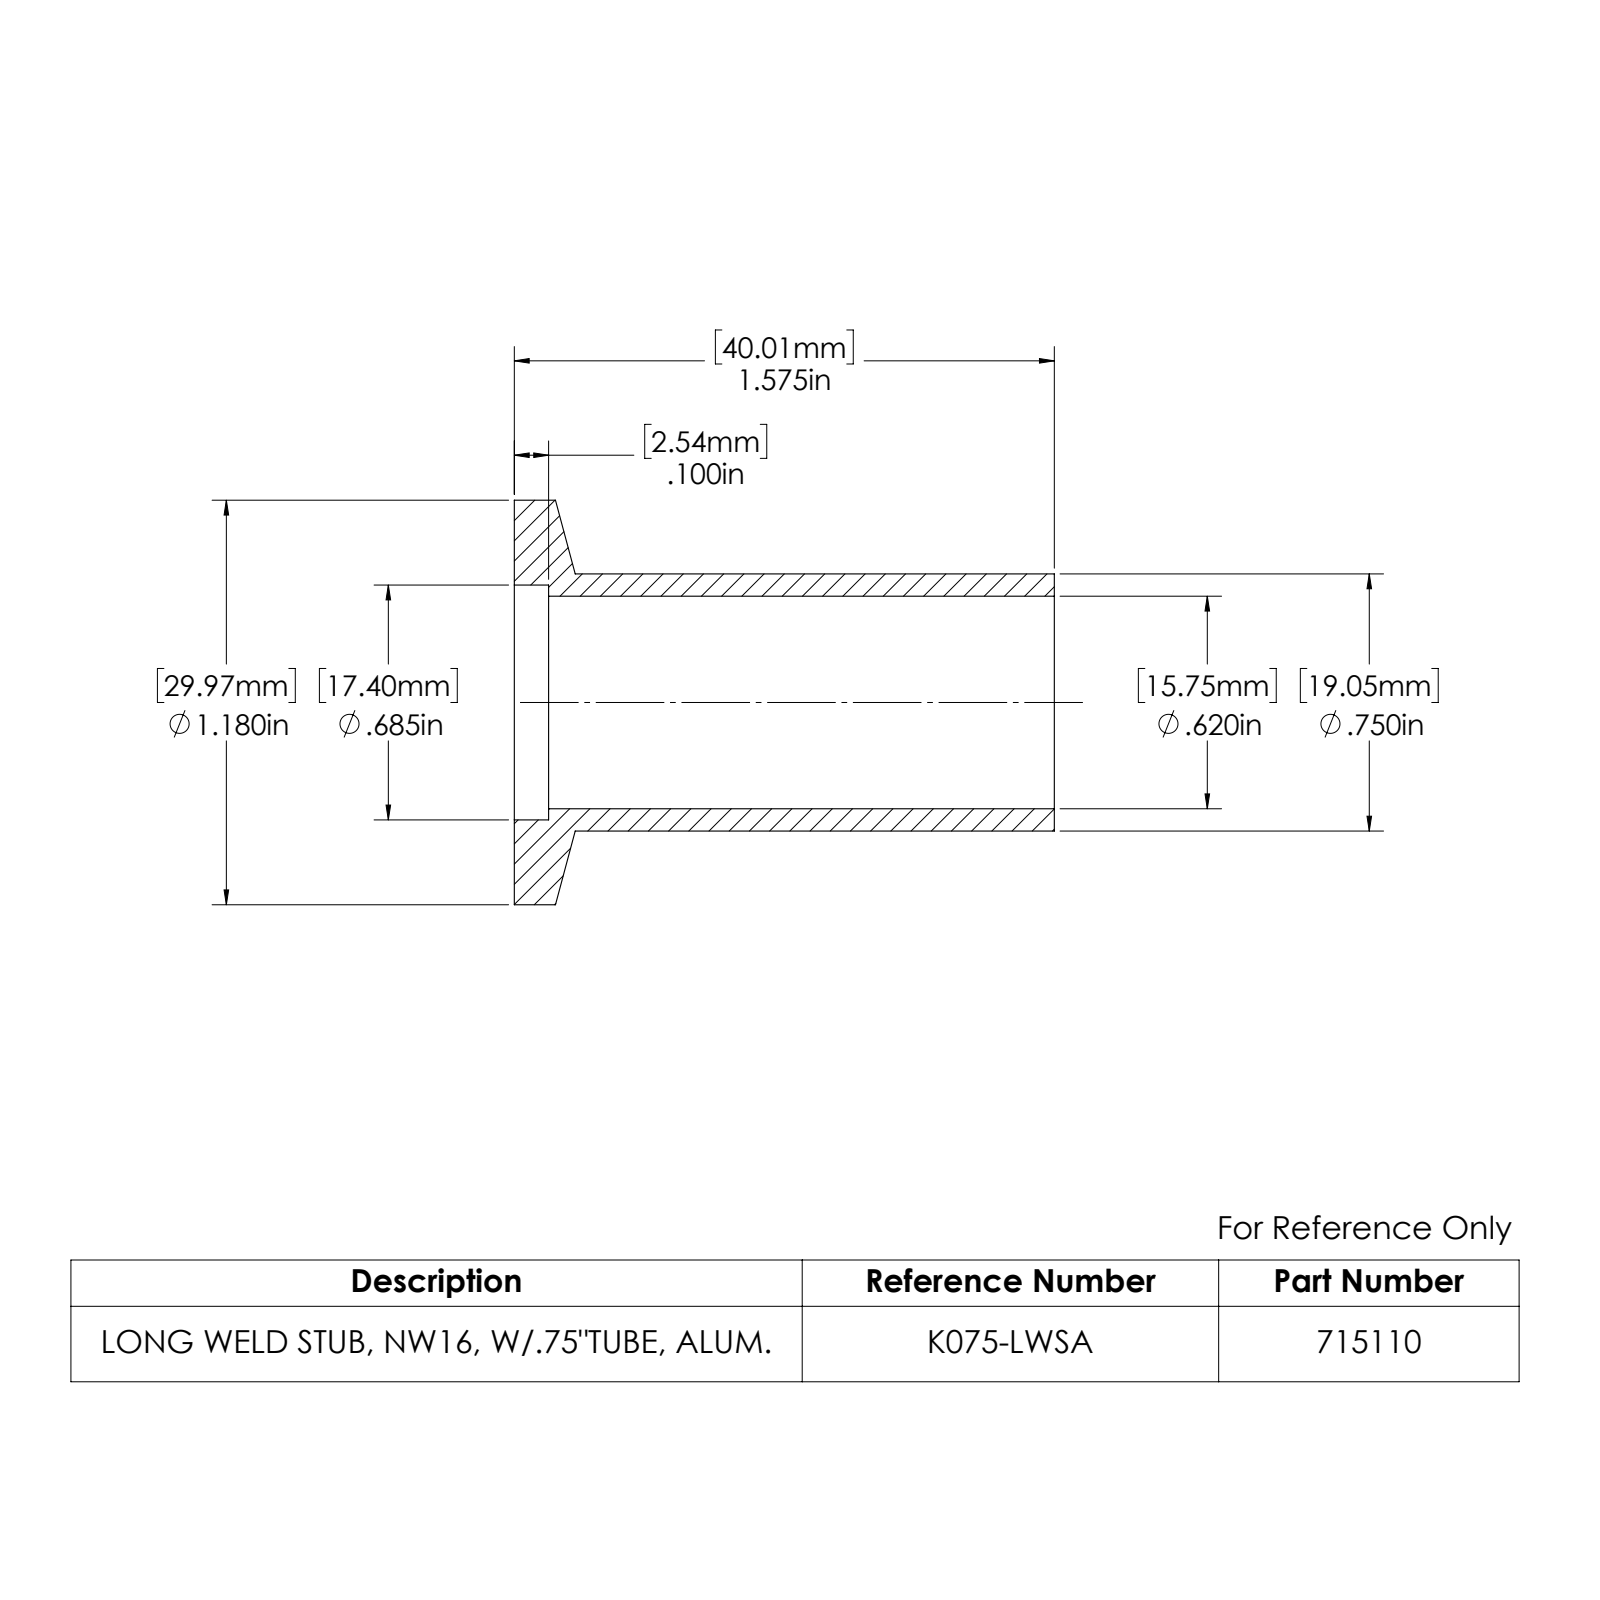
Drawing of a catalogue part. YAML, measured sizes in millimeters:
part_name: "715110"
step_written_by: "SolidWorks 2022 (AUTOMOTIVE_DESIGN)"
units: millimeters
bodies: {solids: 1, faces: 13, planar: 3, cylindrical: 8, other: 2}
overall_size: [40, 30, 30]
volume: 5060
surface_area: 5440
round_holes:
  - {diameter: 15.7, count: 1}
  - {diameter: 17.4, count: 1}
round_bosses_or_shafts:
  - {diameter: 30, count: 1}
  - {diameter: 19.1, count: 1}
face_to_face_distances: [40, 37.5, 2.5]
